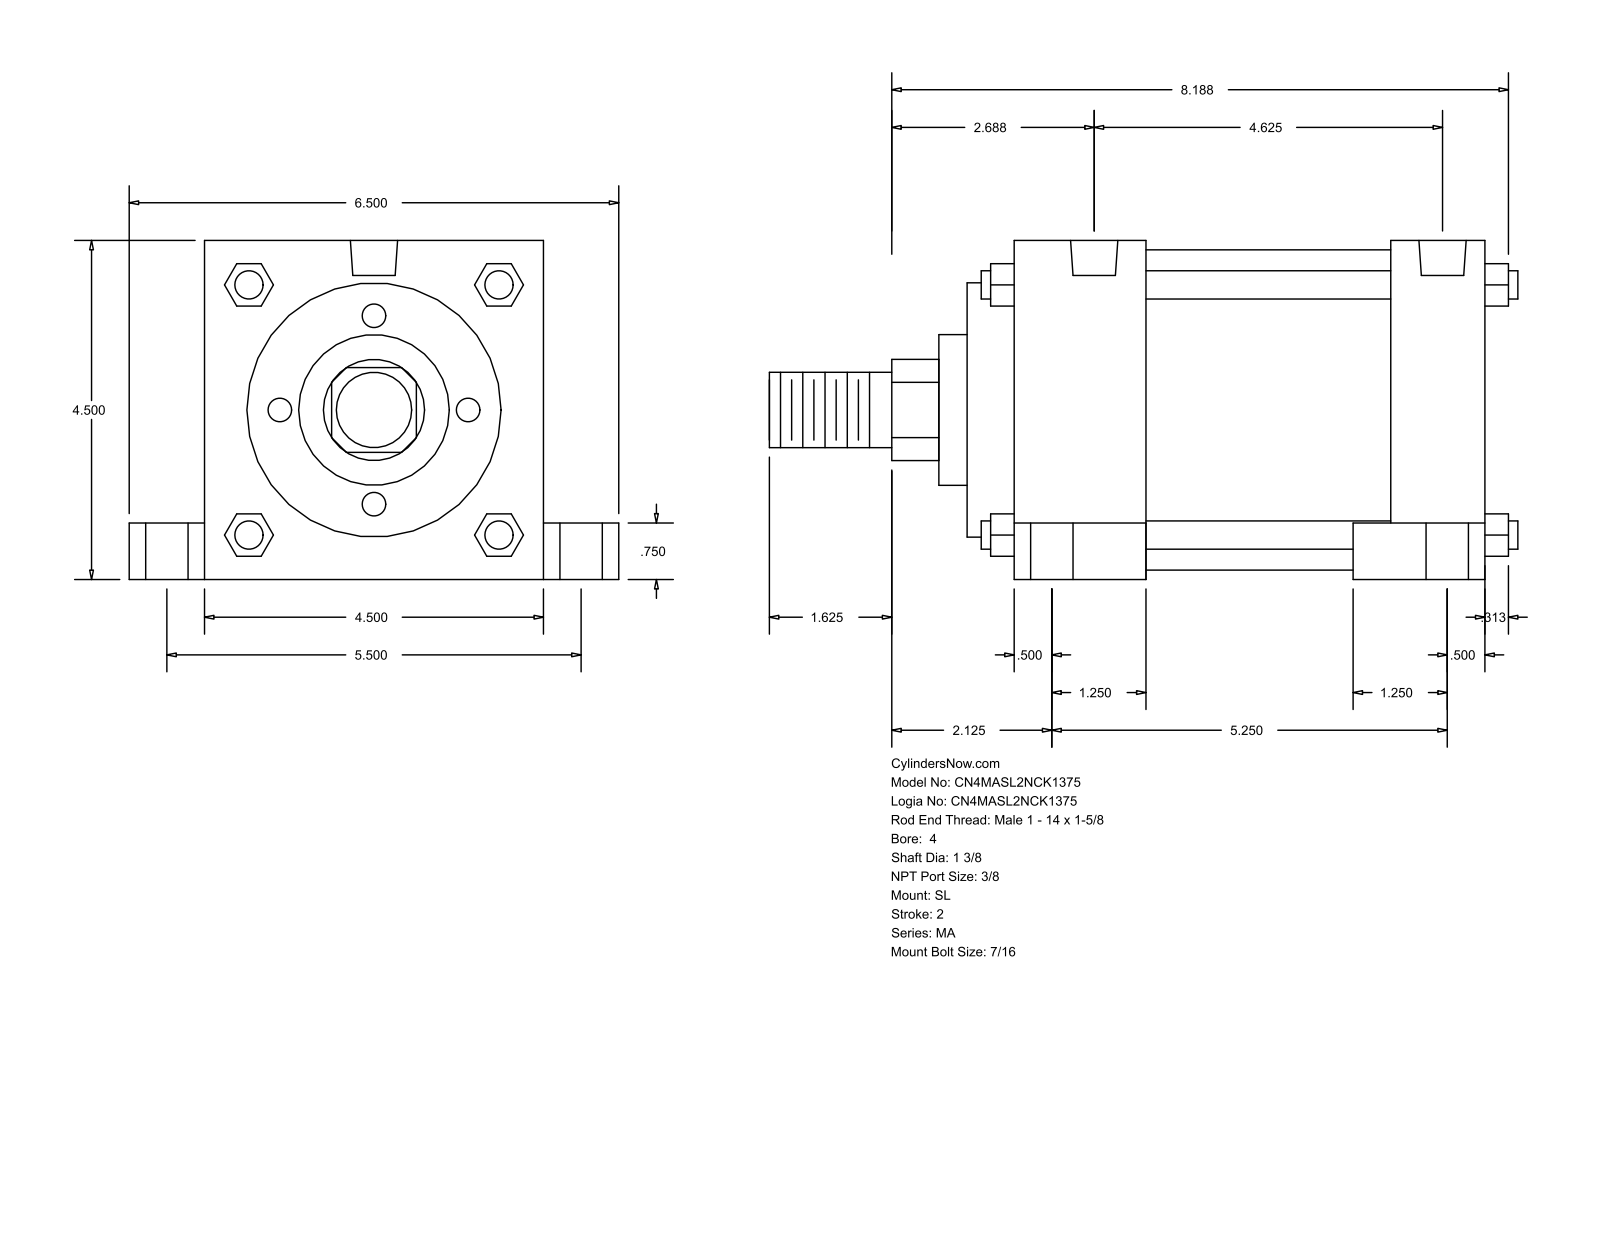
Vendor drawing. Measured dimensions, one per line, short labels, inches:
name: MA_SL__0400_1.375
written by: GSSL Pune (CONFIG_CONTROL_DESIGN)
unit: in
bodies: 0 solids, 150 faces (113 planar, 37 cylindrical, 0 other)
size: 9.937 × 6.5 × 4.5
holes: 4× ⌀0.437, 4× ⌀0.563, 4× ⌀0.813, 2× ⌀0.627
bosses: 4× ⌀0.375, 1× ⌀4.25, 1× ⌀3.375, 1× ⌀2, 1× ⌀1.375, 1× ⌀1
rounds: 1× R0.672
face distances: 4.5, 6.25, 0.625, 6.875, 2.375, 1.75, 4.5, 5.625, 5, 3.25
hole spacings: 0.188, 2.751, 2.761, 2.807, 2.85, 4.25, 4.437, 5.25
